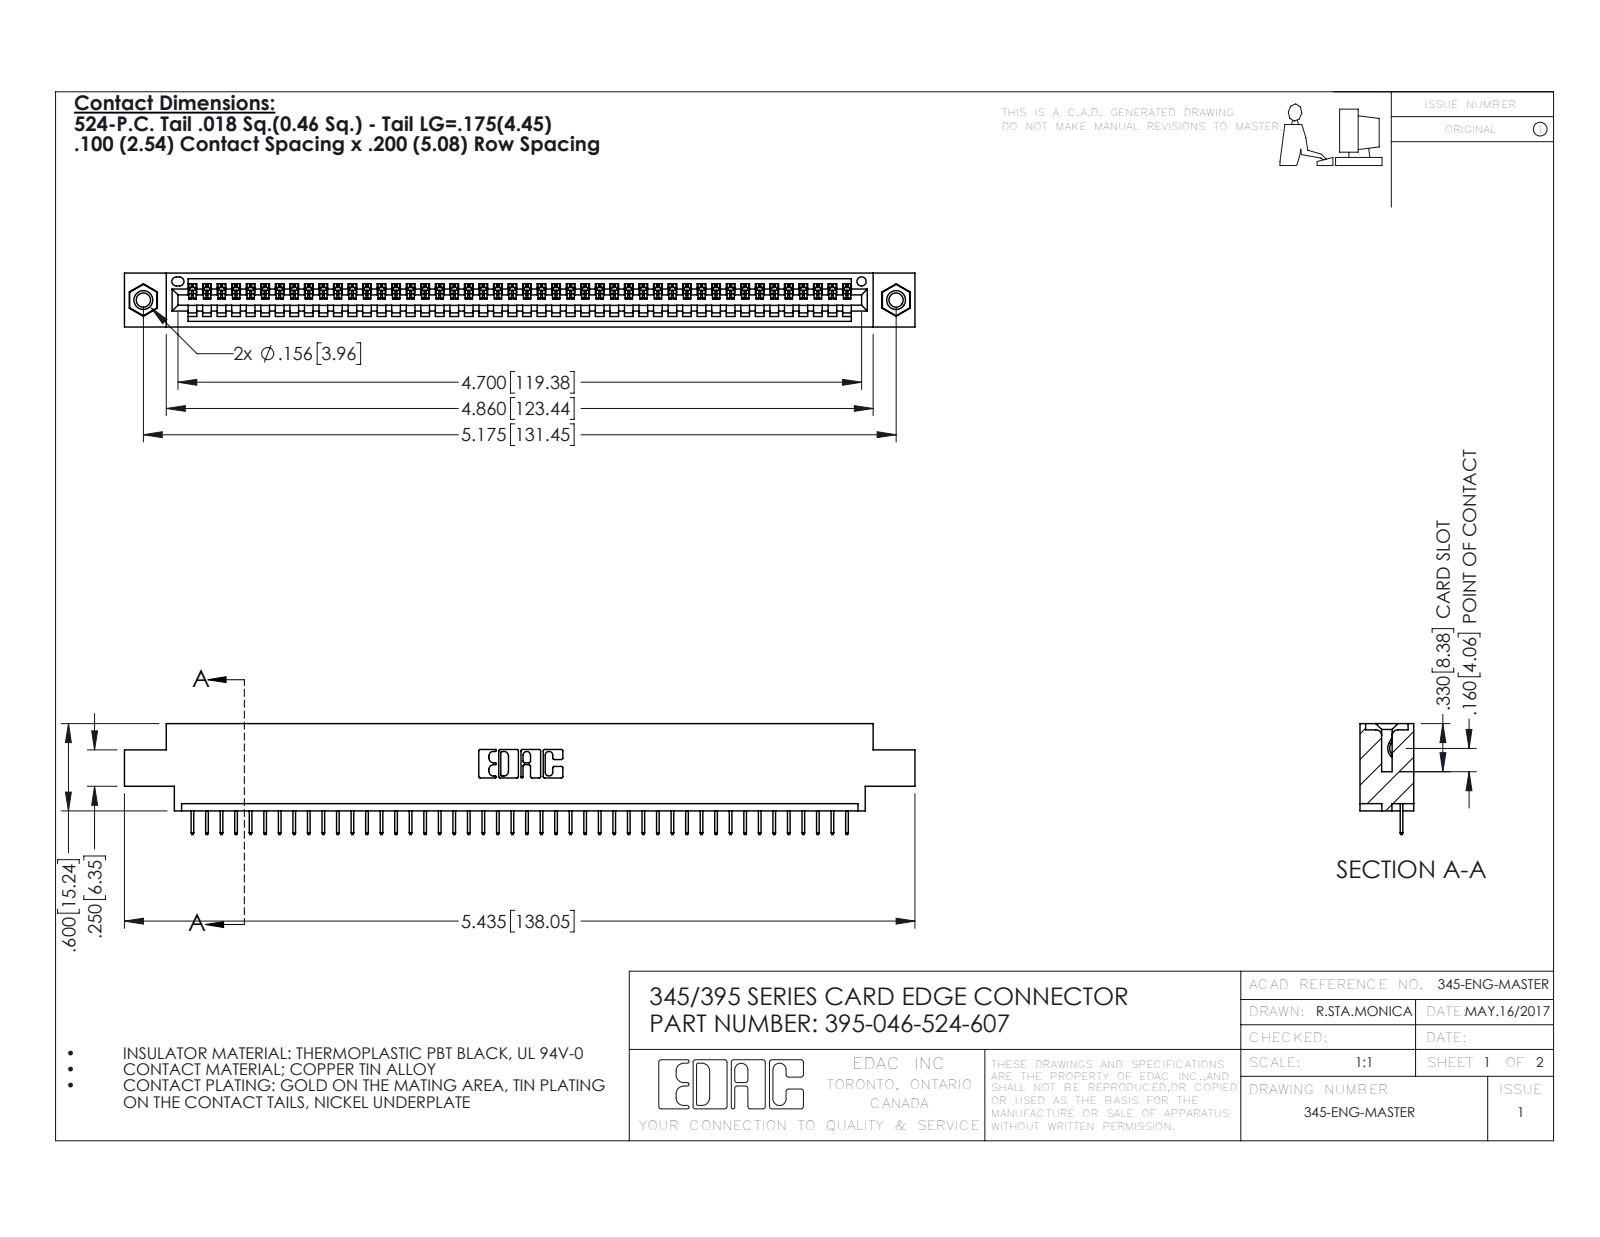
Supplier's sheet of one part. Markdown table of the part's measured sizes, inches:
| quantity | value |
| --- | --- |
| part name | 395-046-524-607; 345-250-001_345-250-005-103; 345-292-001_345-293-124; 345 Part_0.170 Offset - 0.156 Dia-TI |
| STEP written by | SolidWorks 2016 (CONFIG_CONTROL_DESIGN) |
| units | inches |
| bodies | 49 solids, 3042 faces (2232 planar, 794 cylindrical, 16 other) |
| overall size | 5.435 × 0.762 × 0.37 |
| volume | 0.783 in³ |
| surface area | 25.87 in² |
| round holes (diameter × count) | 0.098 × 2, 0.125 × 2, 0.156 × 2, 0.064 × 1 |
| round bosses / shafts (diameter × count) | 0.155 × 2 |
| partial cylindrical surfaces (radius × count) | 0.006 × 92, 0.01 × 22, 0.007 × 6, 0.031 × 6, 0.026 × 3, 0.031 × 2, 0.04 × 2, 0.014 × 1 |
| main face-to-face distances | 0.072, 0.298, 0.37, 0.2, 0.098, 0.272, 0.025, 0.225, 0.072, 0.175 |
| hole center spacings | 0.27, 4.939, 5.175 |
